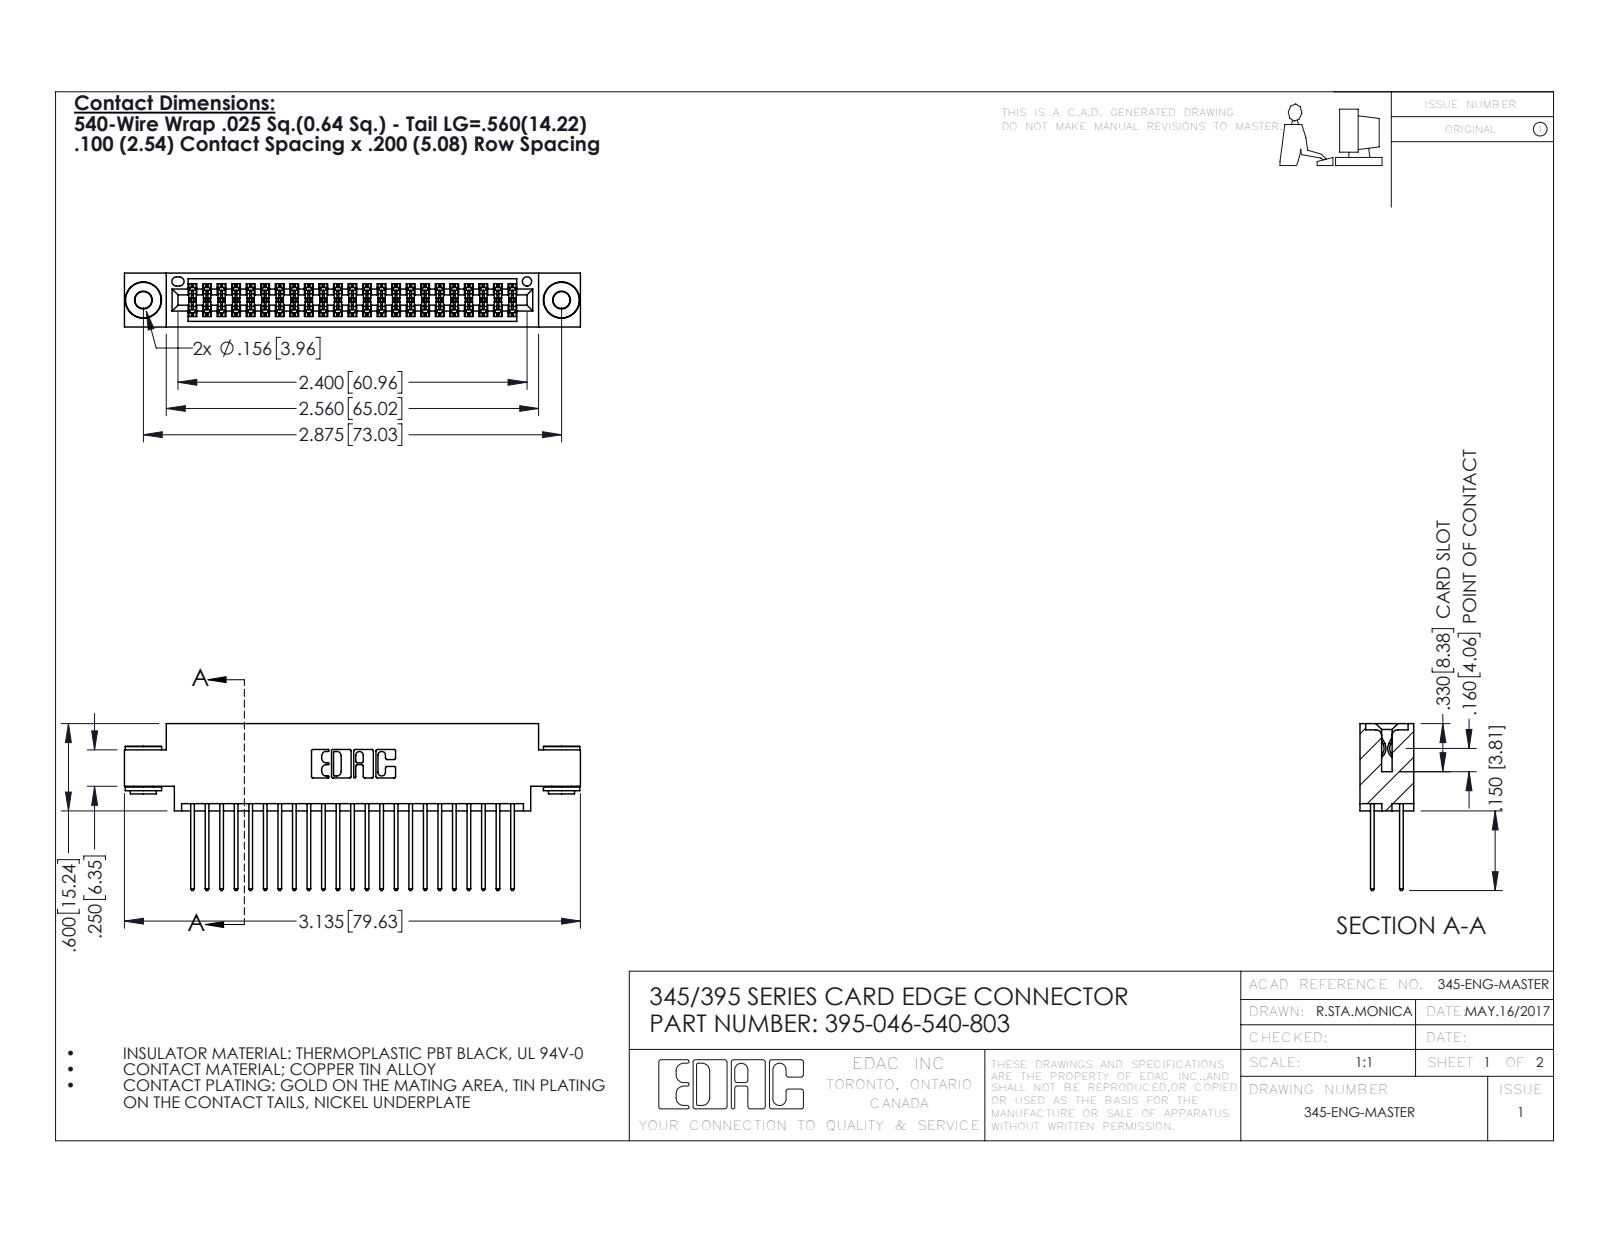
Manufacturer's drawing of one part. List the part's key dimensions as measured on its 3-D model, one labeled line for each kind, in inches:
Part name (STEP PRODUCT): 345 Part_0.170 Offset - 0.156 Dia-TH; 395-046-540-803; 345-292-001_345-293-140; 345-250-002_345-250-002-102
STEP written by: SolidWorks 2016 (CONFIG_CONTROL_DESIGN)
Units: inches
Bodies: 49 solids, 2468 faces (1612 planar, 848 cylindrical, 8 other)
Overall size (bounding box): 3.135 × 1.147 × 0.37
Volume: 0.466 in³ · Surface area: 18.73 in²
Round holes (diameter × count): ⌀0.116 ×2, ⌀0.156 ×2, ⌀0.064 ×1
Round bosses / shafts (diameter × count): ⌀0.25 ×2, ⌀0.18 ×2, ⌀0.136 ×2
Partial cylindrical surfaces — rounded edges, fillets, slot ends (radius × count): R0.006 ×69, R0.01 ×46, R0.01 ×22, R0.007 ×6, R0.031 ×6, R0.026 ×3, R0.014 ×2, R0.019 ×2
Main face-to-face distances: 0.072, 0.298, 0.2, 0.098, 0.272, 0.025, 0.37, 0.225, 0.175, 0.1
Hole centre spacings: 0.27, 2.641, 2.875
